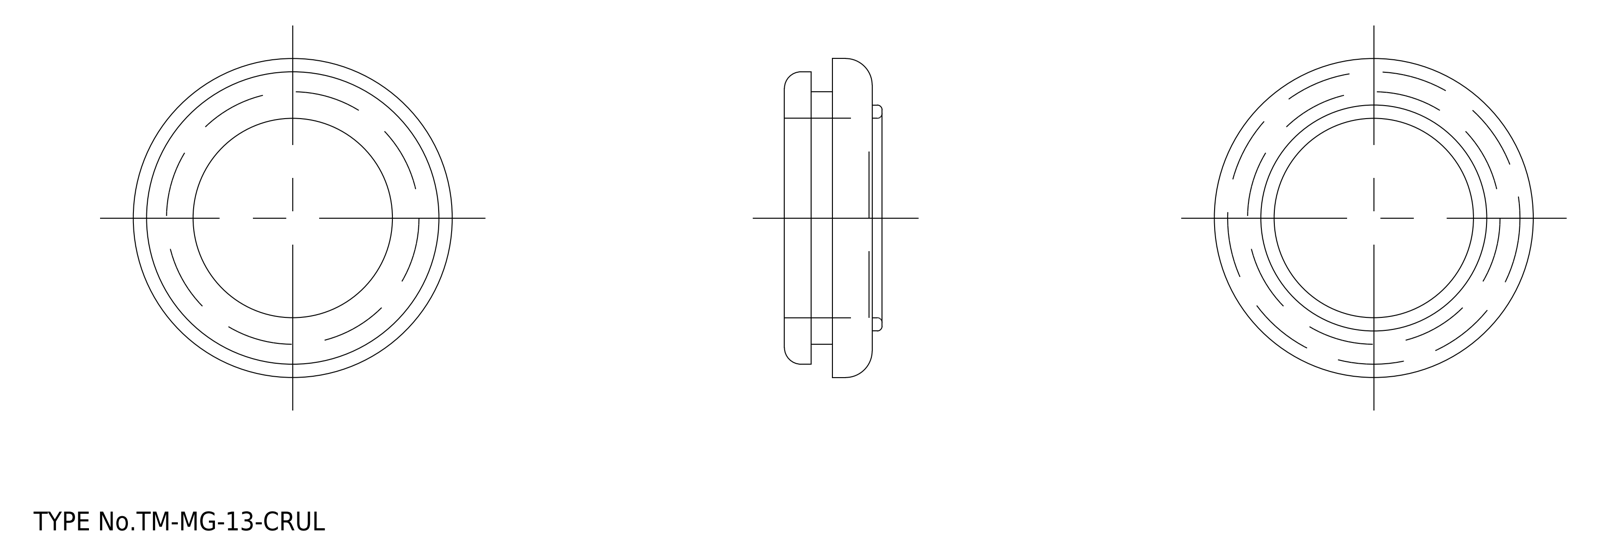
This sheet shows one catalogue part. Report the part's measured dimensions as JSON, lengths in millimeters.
{"step_written_by": "spGate 15.6.1 (AUTOMOTIVE_DESIGN)", "units": "millimeters", "bodies": {"solids": 1, "faces": 27, "planar": 7, "cylindrical": 12, "other": 8}, "overall_size": [48, 48, 14.4], "volume_mm3": 11135, "surface_area_mm2": 7190, "round_holes": [[30, 1]], "round_bosses_or_shafts": [[48, 1], [44, 1], [38, 1], [34, 1]], "face_to_face_distances": [0.5, 5.5, 6, 7.2, 12.7, 13.2, 4, 3.2, 8.7, 9.2]}
